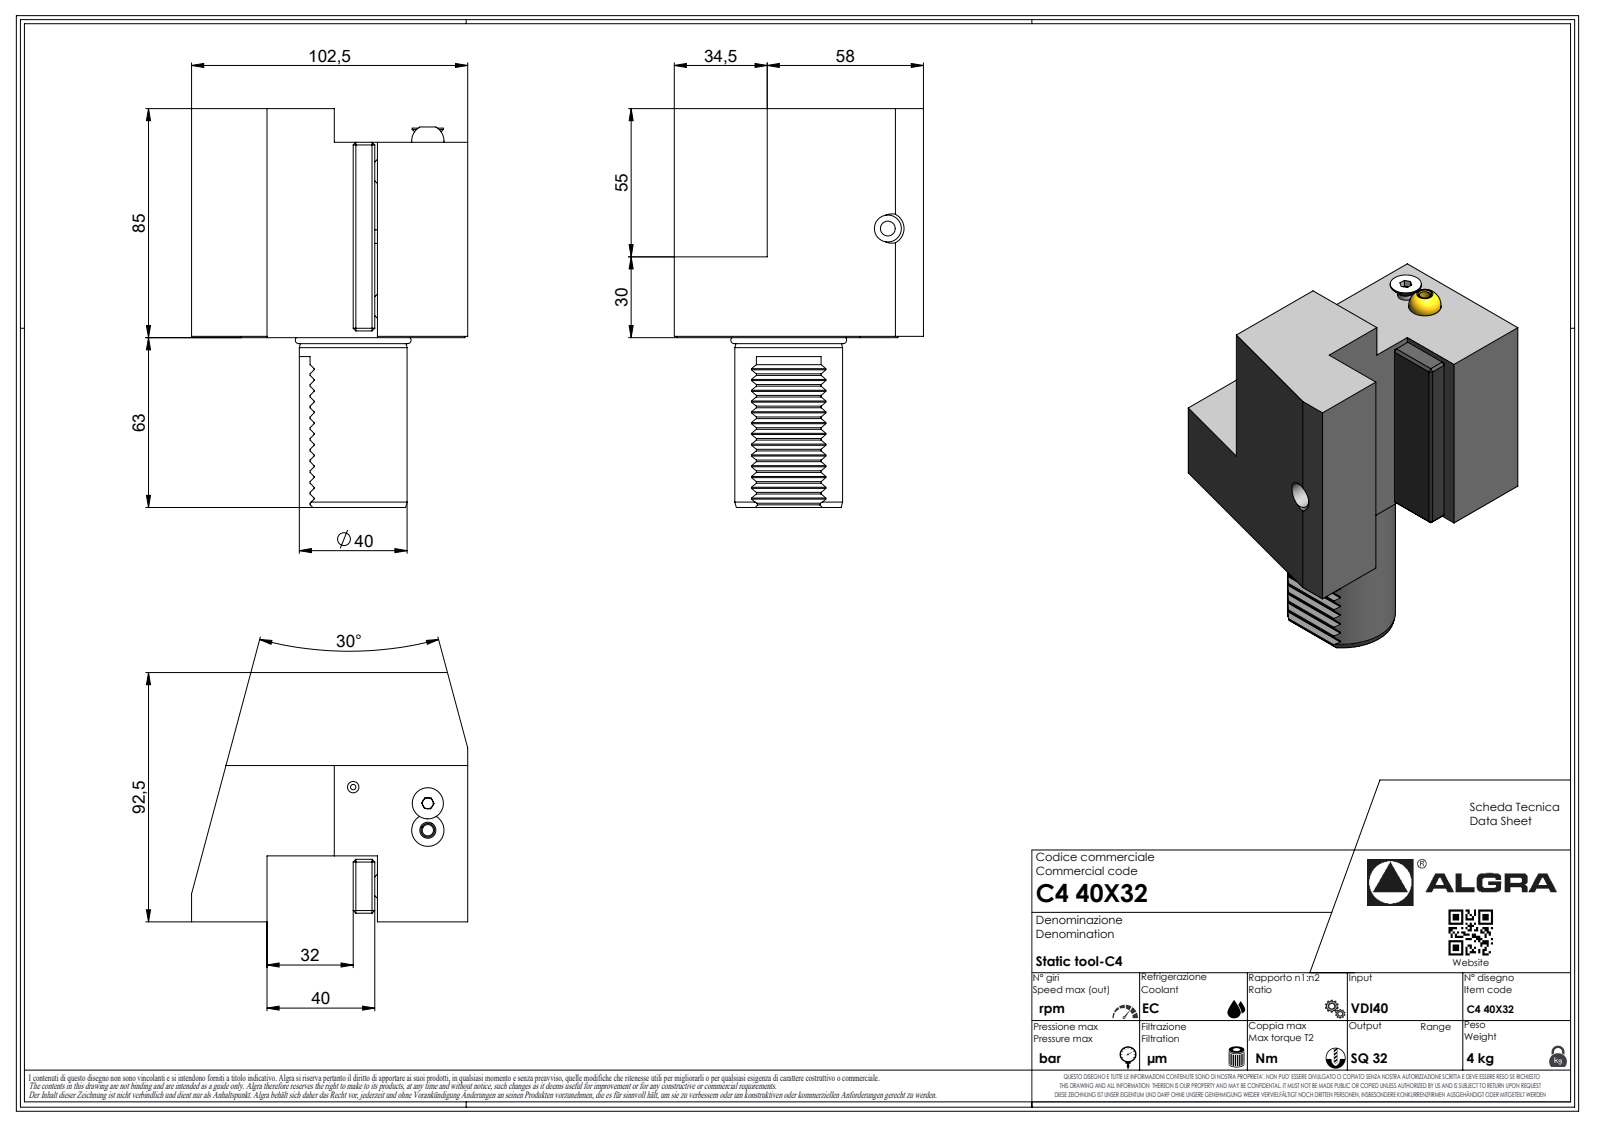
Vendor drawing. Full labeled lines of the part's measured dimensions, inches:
Part name (STEP PRODUCT): C440X32
STEP written by: SolidWorks 2023 (AUTOMOTIVE_DESIGN)
Units: inches
Bodies: 1 solid, 328 faces (234 planar, 43 cylindrical, 51 other)
Overall size (bounding box): 5.827 × 4.035 × 3.642
Volume: 32.5 in³ · Surface area: 89.09 in²
Round holes (diameter × count): ⌀0.083 ×1
Round bosses / shafts (diameter × count): ⌀3.268 ×1, ⌀1.575 ×1, ⌀1.524 ×1, ⌀0.251 ×1, ⌀0.197 ×1, ⌀0.067 ×1
Partial cylindrical surfaces — rounded edges, fillets, slot ends (radius × count): R0.012 ×13, R0.013 ×7, R0.02 ×7, R0.146 ×7, R0.008 ×1
Main face-to-face distances: 1.319, 2.283, 1.673, 0.965, 1.358, 2.677, 1.181, 0.02, 1.161, 2.854
